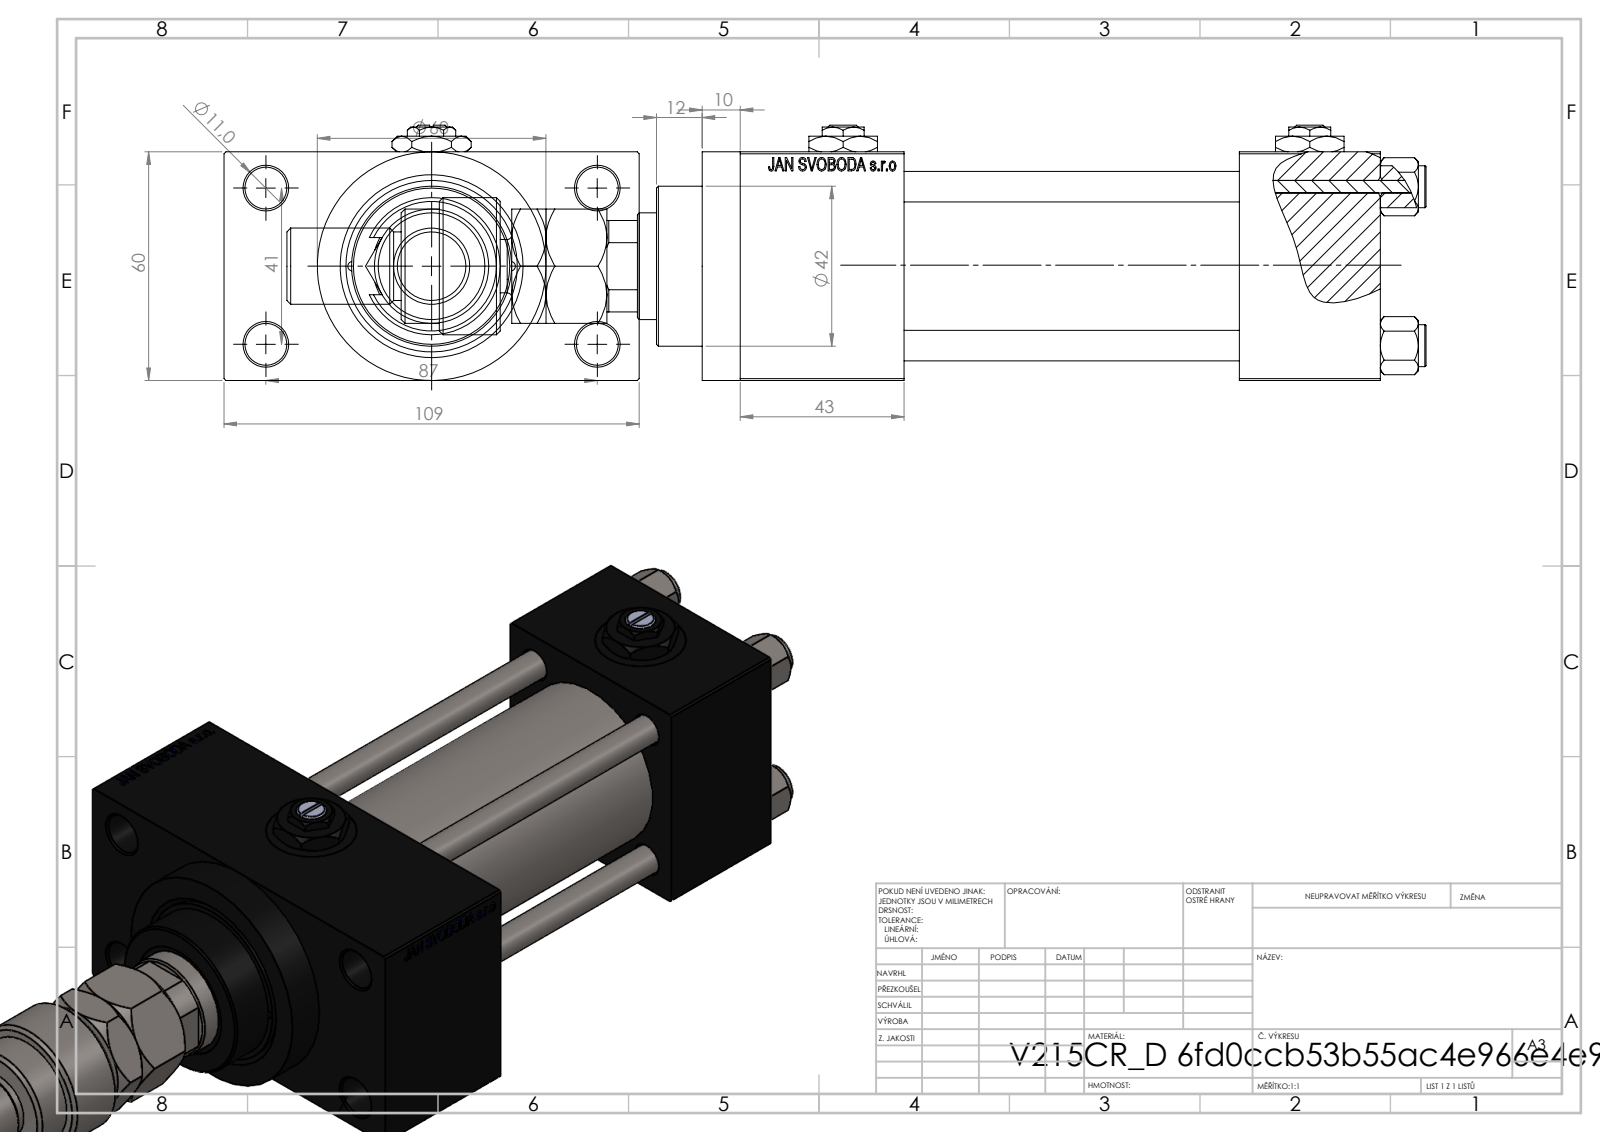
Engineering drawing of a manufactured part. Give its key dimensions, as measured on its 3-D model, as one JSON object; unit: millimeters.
{"part_name": "V215CR_D_TYCINKA; V215CR_VCP_D; MFA; NUT_M5_D (+4 more)", "step_written_by": "SolidWorks 2019 (CONFIG_CONTROL_DESIGN)", "units": "millimeters", "bodies": {"solids": 15, "faces": 1300, "planar": 578, "cylindrical": 116, "other": 606}, "overall_size": [299, 109, 67], "volume_mm3": 612061, "surface_area_mm2": 158724, "round_holes": [[8, 4], [11, 4], [16.66, 4], [24, 4], [7, 3], [2.5, 2], [18.5, 1], [28, 1], [31, 1], [40, 1], [45, 1]], "round_bosses_or_shafts": [[11, 4], [60, 1], [46, 1], [42, 1], [36, 1], [30, 1], [22, 1], [20, 1]], "partial_cylinders_radius": [[7.5, 1], [12, 1], [13.5, 1]], "face_to_face_distances": [60, 88, 24.5, 84.5, 37, 125, 43, 168, 131, 109], "hole_center_spacings": [20.85, 22.65, 29.49, 30.62, 41.7, 46.53, 47.15, 48.09]}
